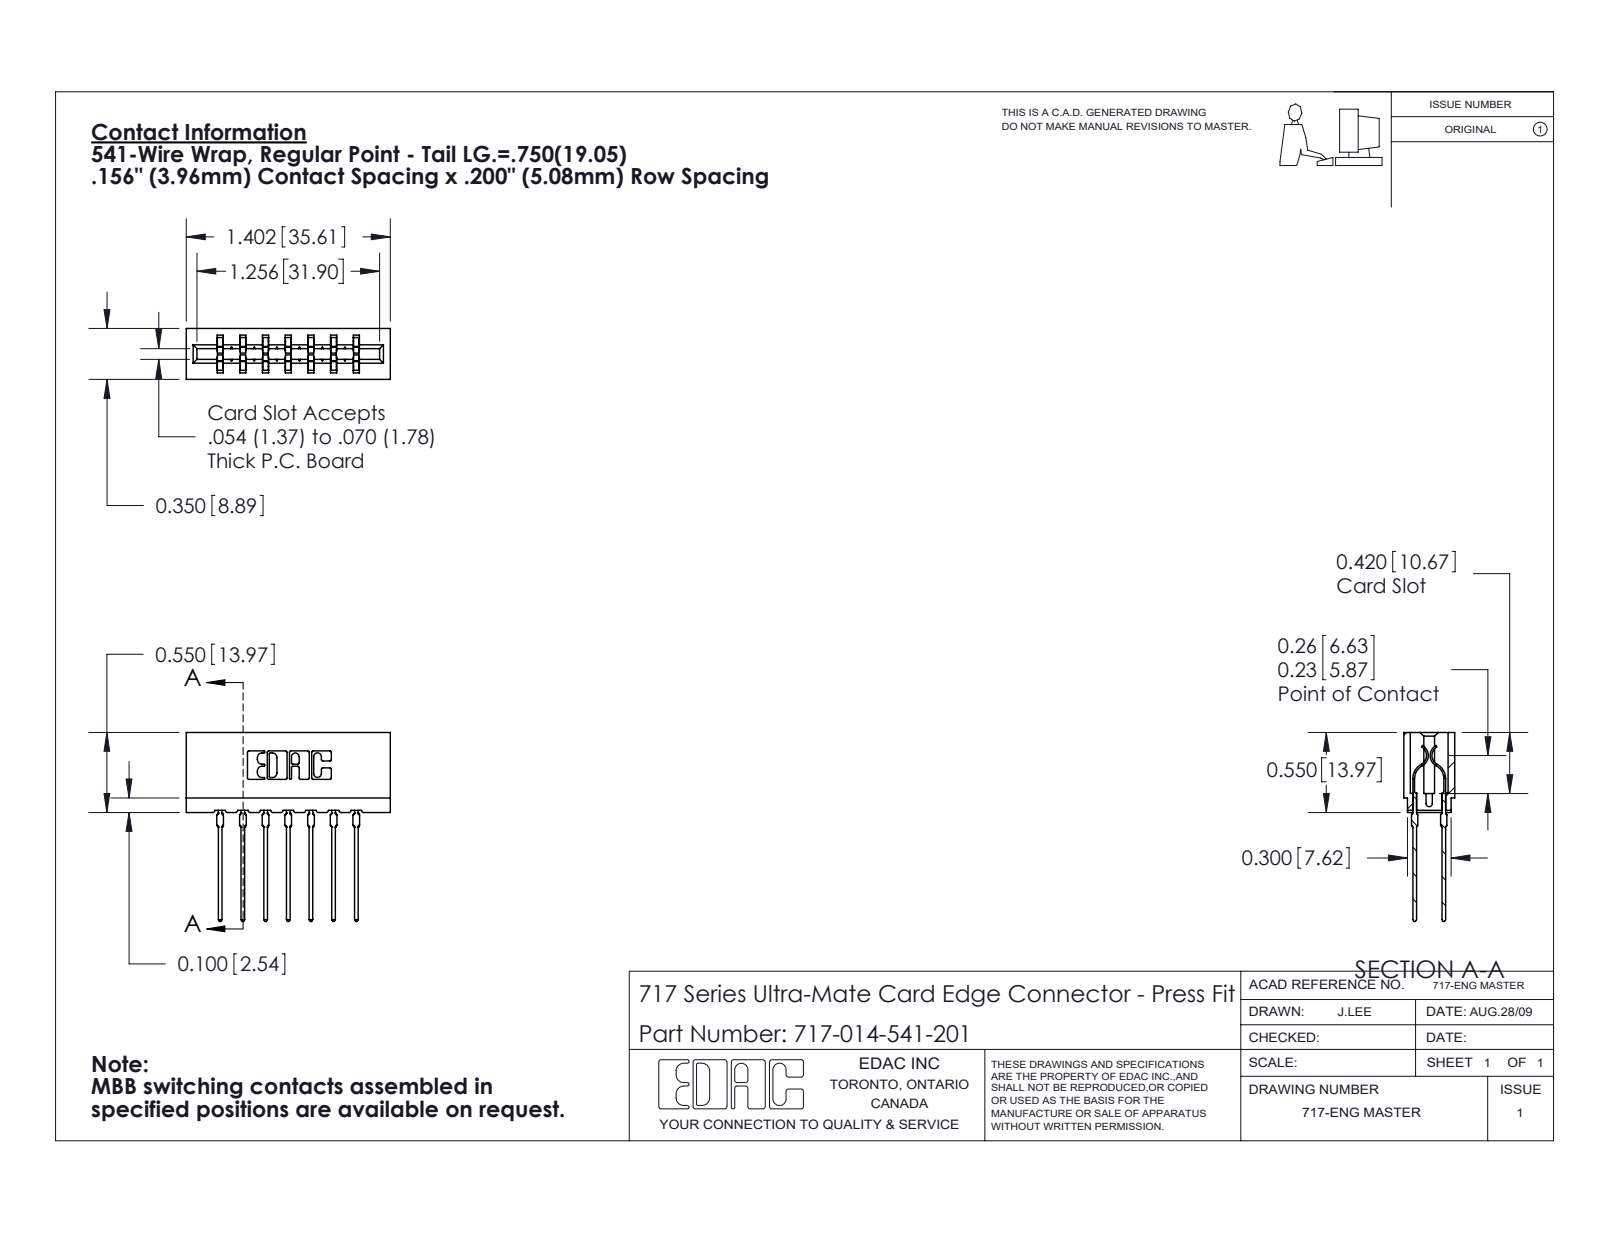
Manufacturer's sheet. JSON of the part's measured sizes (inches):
{"part_name": "745-292-001_541; 717-014-541-201; 717 Part_Insulator Option - 06", "step_written_by": "SolidWorks 2020 (CONFIG_CONTROL_DESIGN)", "units": "inches", "bodies": {"solids": 15, "faces": 1354, "planar": 705, "cylindrical": 285, "other": 364}, "overall_size": [1.402, 1.299, 0.35], "volume_in3": 0.201, "surface_area_in2": 7.577, "partial_cylinders_radius": [[0.021, 28], [0.01, 22], [0.015, 14], [0.005, 8], [0.011, 8], [0.007, 6], [0.031, 6], [0.026, 3]], "face_to_face_distances": [0.212, 0.156, 0.138, 0.35, 0.198, 0.312, 0.468, 0.624, 0.063, 0.287]}
